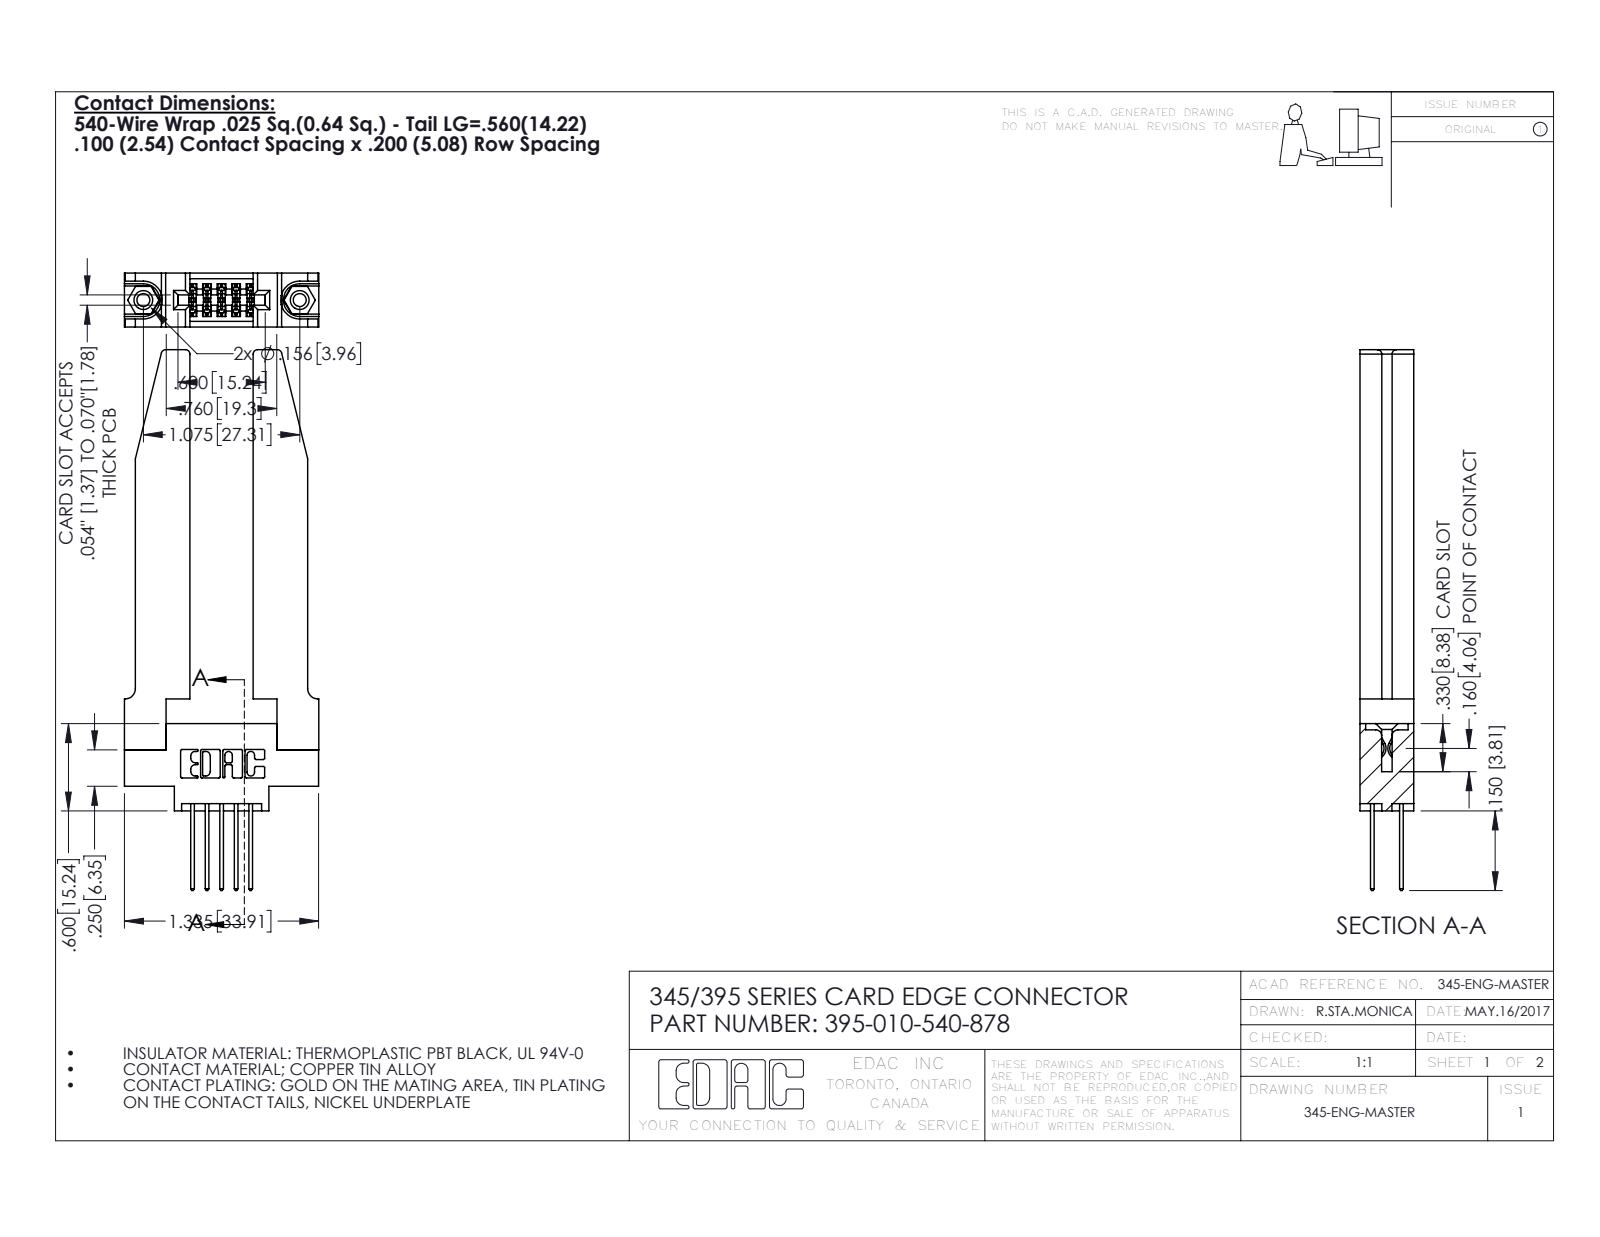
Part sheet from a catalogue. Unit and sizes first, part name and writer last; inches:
Units: inches
Overall size (bounding box): 3.717 × 1.336 × 0.37
Round holes (diameter × count): ⌀0.089 ×2, ⌀0.125 ×2, ⌀0.156 ×2, ⌀0.064 ×1
Round bosses / shafts (diameter × count): ⌀0.155 ×2
Partial cylindrical surfaces — rounded edges, fillets, slot ends (radius × count): R0.01 ×22, R0.006 ×15, R0.01 ×10, R0.03 ×8, R0.007 ×6, R0.031 ×6, R0.026 ×3, R0.014 ×2
Main face-to-face distances: 0.37, 0.15, 0.22, 0.148, 0.072, 0.435, 0.298, 0.077, 0.095, 0.2
Hole centre spacings: 0.27, 0.847, 1.075
Volume: 0.65 in³ · Surface area: 16.58 in²
Bodies: 15 solids, 864 faces (556 planar, 256 cylindrical, 52 other)
Part name (STEP PRODUCT): 345-220-078_345-220-078; 395-010-540-878; 345 Part_0.170 Offset - 0.156 Dia-TH; 345-250-001_345-250-001-102 (+1 more)
STEP written by: SolidWorks 2016 (CONFIG_CONTROL_DESIGN)
